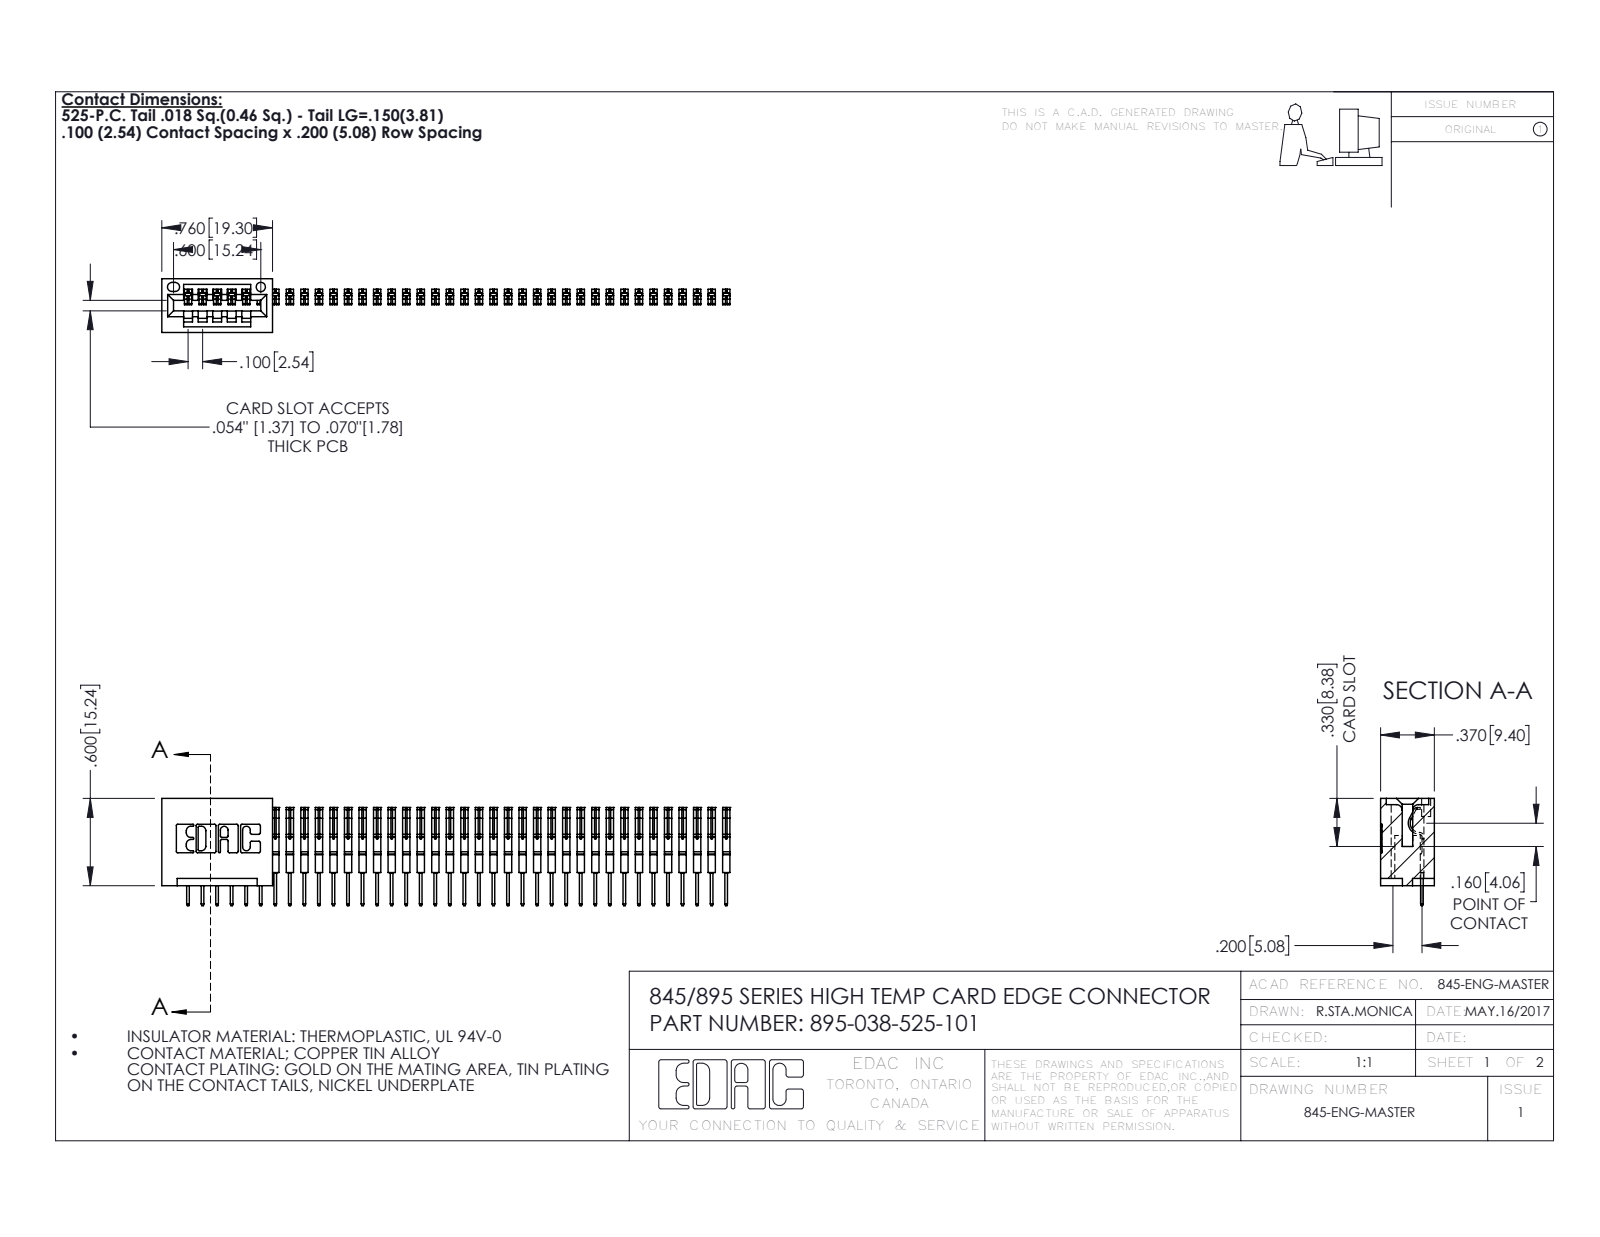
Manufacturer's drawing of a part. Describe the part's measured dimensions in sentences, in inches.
The part is named "895-038-525-101; 345-292-001_345-293-125; 845 Part_No Mounting Lugs". Its 3-D file was written by "SolidWorks 2020 (CONFIG_CONTROL_DESIGN)". It is 39 solids with 2474 faces: 1824 planar, 650 cylindrical and 0 other. Overall it measures 4.06 by 0.737 by 0.37 inches. Its volume is 0.622 cubic inches and its surface area 20.4 square inches. Round holes: 1 of diameter 0.064. Partial cylindrical surfaces (rounded edges, fillets, slot ends): 76 of radius 0.006, 22 of radius 0.01, 6 of radius 0.007, 6 of radius 0.031, 3 of radius 0.026, 2 of radius 0.031, 2 of radius 0.04, 1 of radius 0.014. The main face-to-face distances are 0.298, 0.072, 0.37, 0.2, 0.098, 0.272, 0.025, 0.225, 0.072, 0.149.
